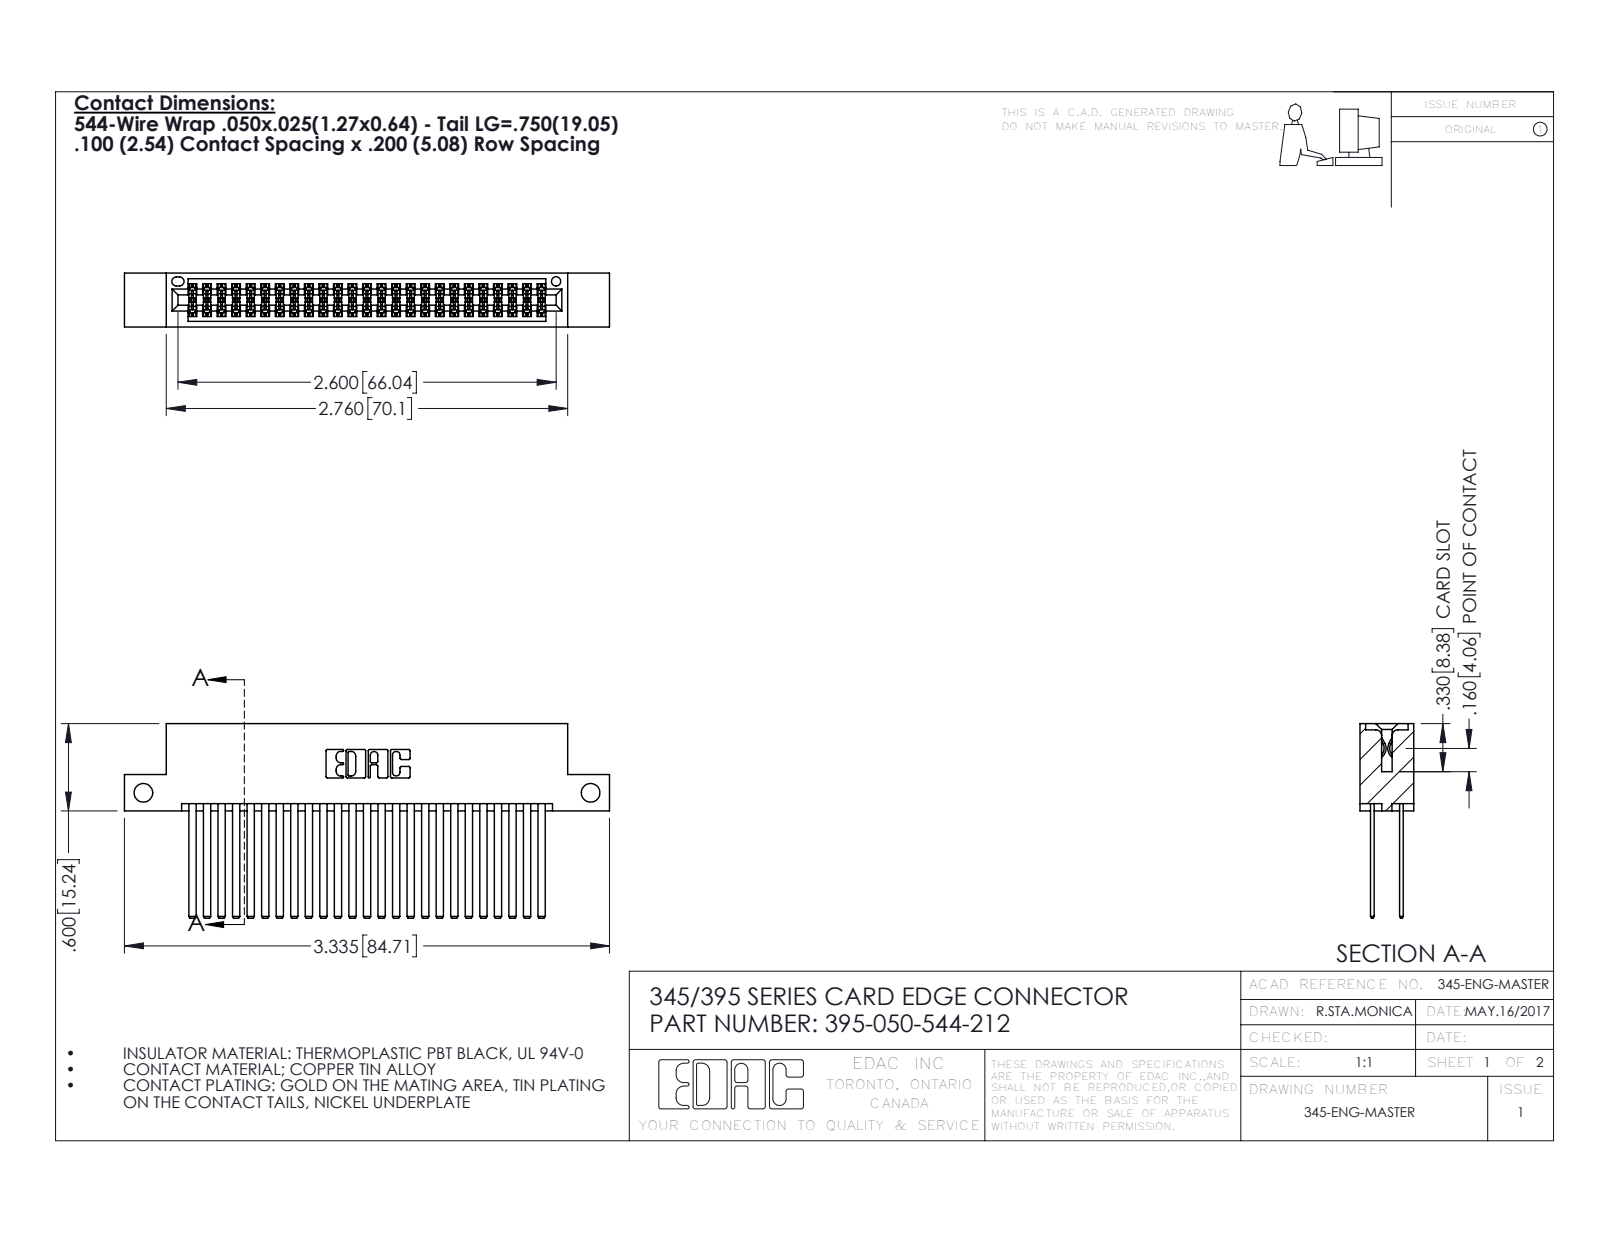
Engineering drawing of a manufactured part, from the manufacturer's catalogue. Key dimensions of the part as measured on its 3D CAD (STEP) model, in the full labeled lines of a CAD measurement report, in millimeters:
Part name (STEP PRODUCT): 345 Part_Flush Mounting Lugs - Side Mount; 345-292-001_345-293-144; 395-050-544-212
STEP written by: SolidWorks 2016 (CONFIG_CONTROL_DESIGN)
Units: millimetres
Bodies: 51 solids, 2326 faces (1530 planar, 796 cylindrical, 0 other)
Overall size (bounding box): 84.7 × 34 × 9.4
Volume: 8 690 mm³ · Surface area: 14 430 mm²
Round holes (diameter × count): ⌀3.3 ×2, ⌀1.6 ×1
Partial cylindrical surfaces — rounded edges, fillets, slot ends (radius × count): R0.2 ×75, R0.3 ×22, R0.2 ×6, R0.8 ×6, R0.7 ×3, R0.4 ×2, R0.5 ×2, R0.6 ×2
Main face-to-face distances: 5.1, 0.6, 7.6, 1.8, 2.5, 6.9, 5.7, 4.4, 9.4, 1.3
Hole centre spacings: 78.1
